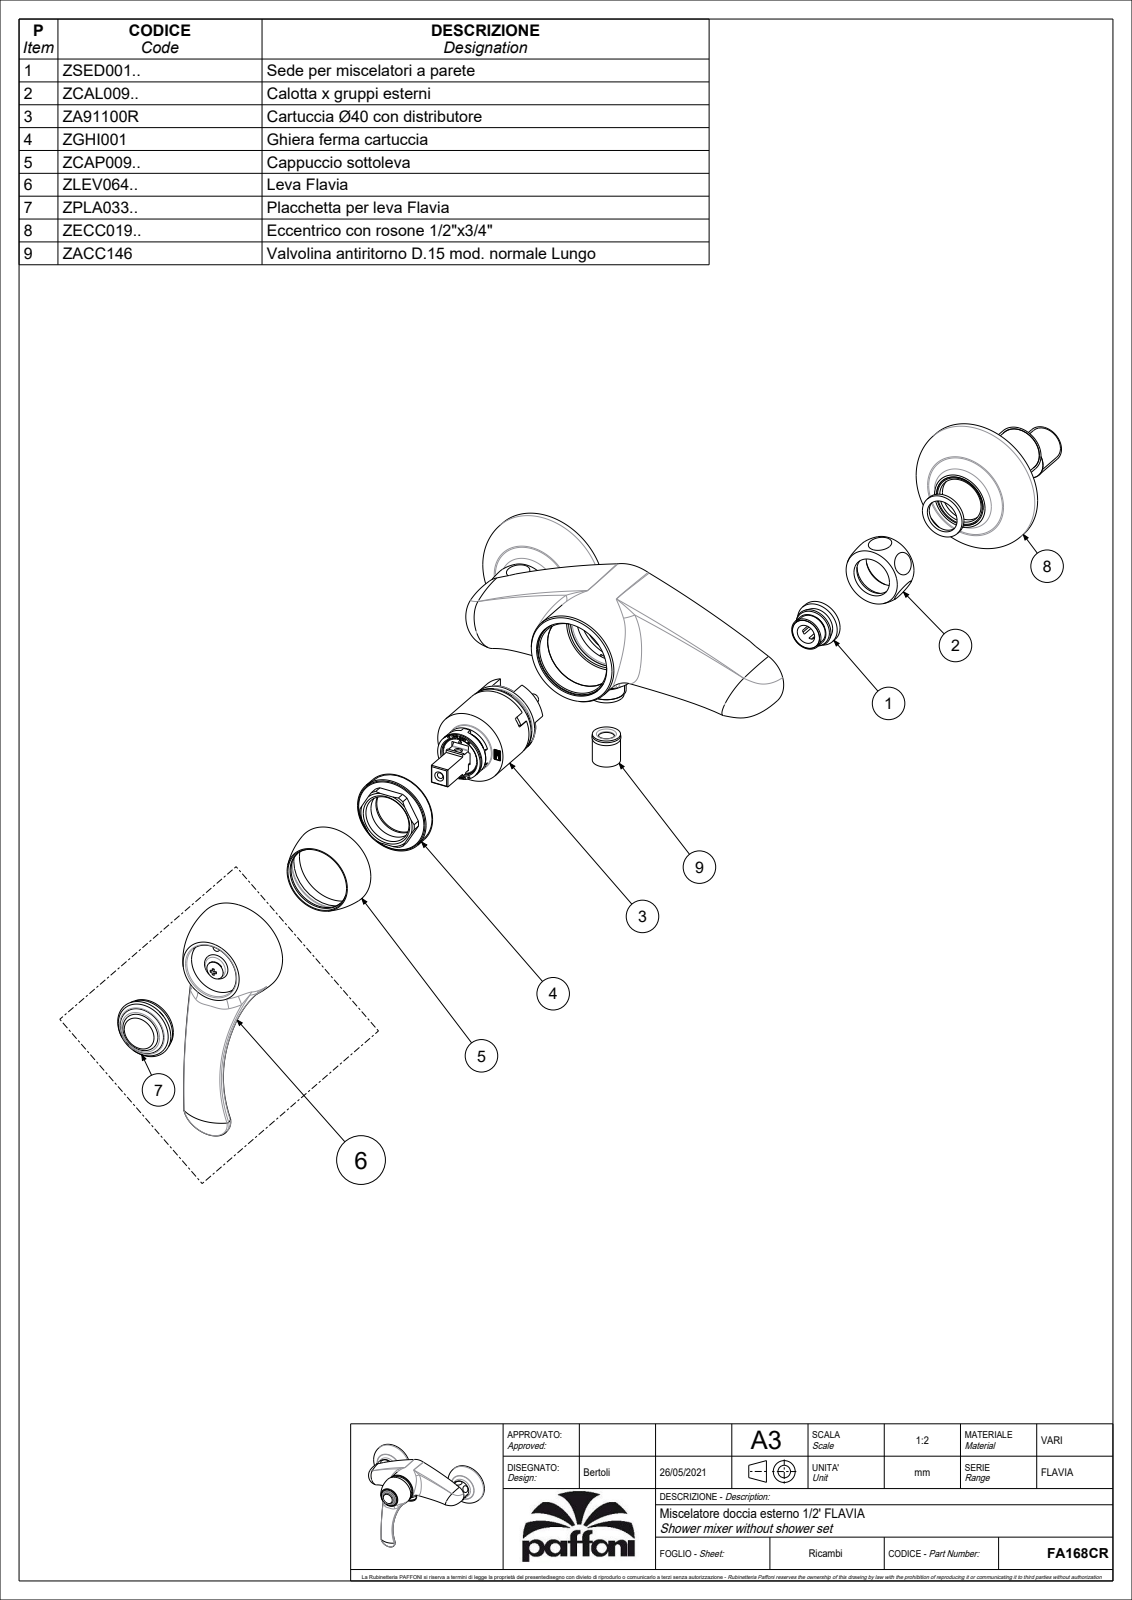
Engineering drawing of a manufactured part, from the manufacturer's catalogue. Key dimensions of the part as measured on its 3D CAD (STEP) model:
Part name (STEP PRODUCT): FA168CR
STEP written by: CREO PARAMETRIC BY PTC INC, 2020044 (CONFIG_CONTROL_DESIGN)
Units: millimetres
Bodies: 3 solids, 1506 faces (738 planar, 394 cylindrical, 374 other)
Overall size (bounding box): 220 × 154.43 × 124.28
Volume: 211 383 mm³ · Surface area: 145 671 mm²
Round holes (diameter × count): ⌀8 ×4, ⌀7 ×3, ⌀4 ×2, ⌀10.5 ×2, ⌀12 ×2, ⌀16.5 ×2, ⌀18 ×2, ⌀21.5 ×2, ⌀24.1 ×2, ⌀25 ×2, ⌀27.5 ×2, ⌀68 ×2
Round bosses / shafts (diameter × count): ⌀70 ×2, ⌀28.14 ×2, ⌀24 ×2, ⌀15.9 ×2, ⌀10 ×2, ⌀9.4 ×2, ⌀50 ×1, ⌀39.5 ×1
Partial cylindrical surfaces — rounded edges, fillets, slot ends (radius × count): R0.5 ×55, R0.2 ×24, R1.5 ×8, R0.3 ×4, R5.5 ×2, R7.5 ×2, R14.5 ×2, R20.5 ×2
Main face-to-face distances: 3.5, 0.5, 11.5, 3, 6.5, 14, 18.5, 32, 13.5, 4
Hole centre spacings: 2, 7.92, 8.6, 8.79, 9.03, 9.9, 10.13, 13.04
